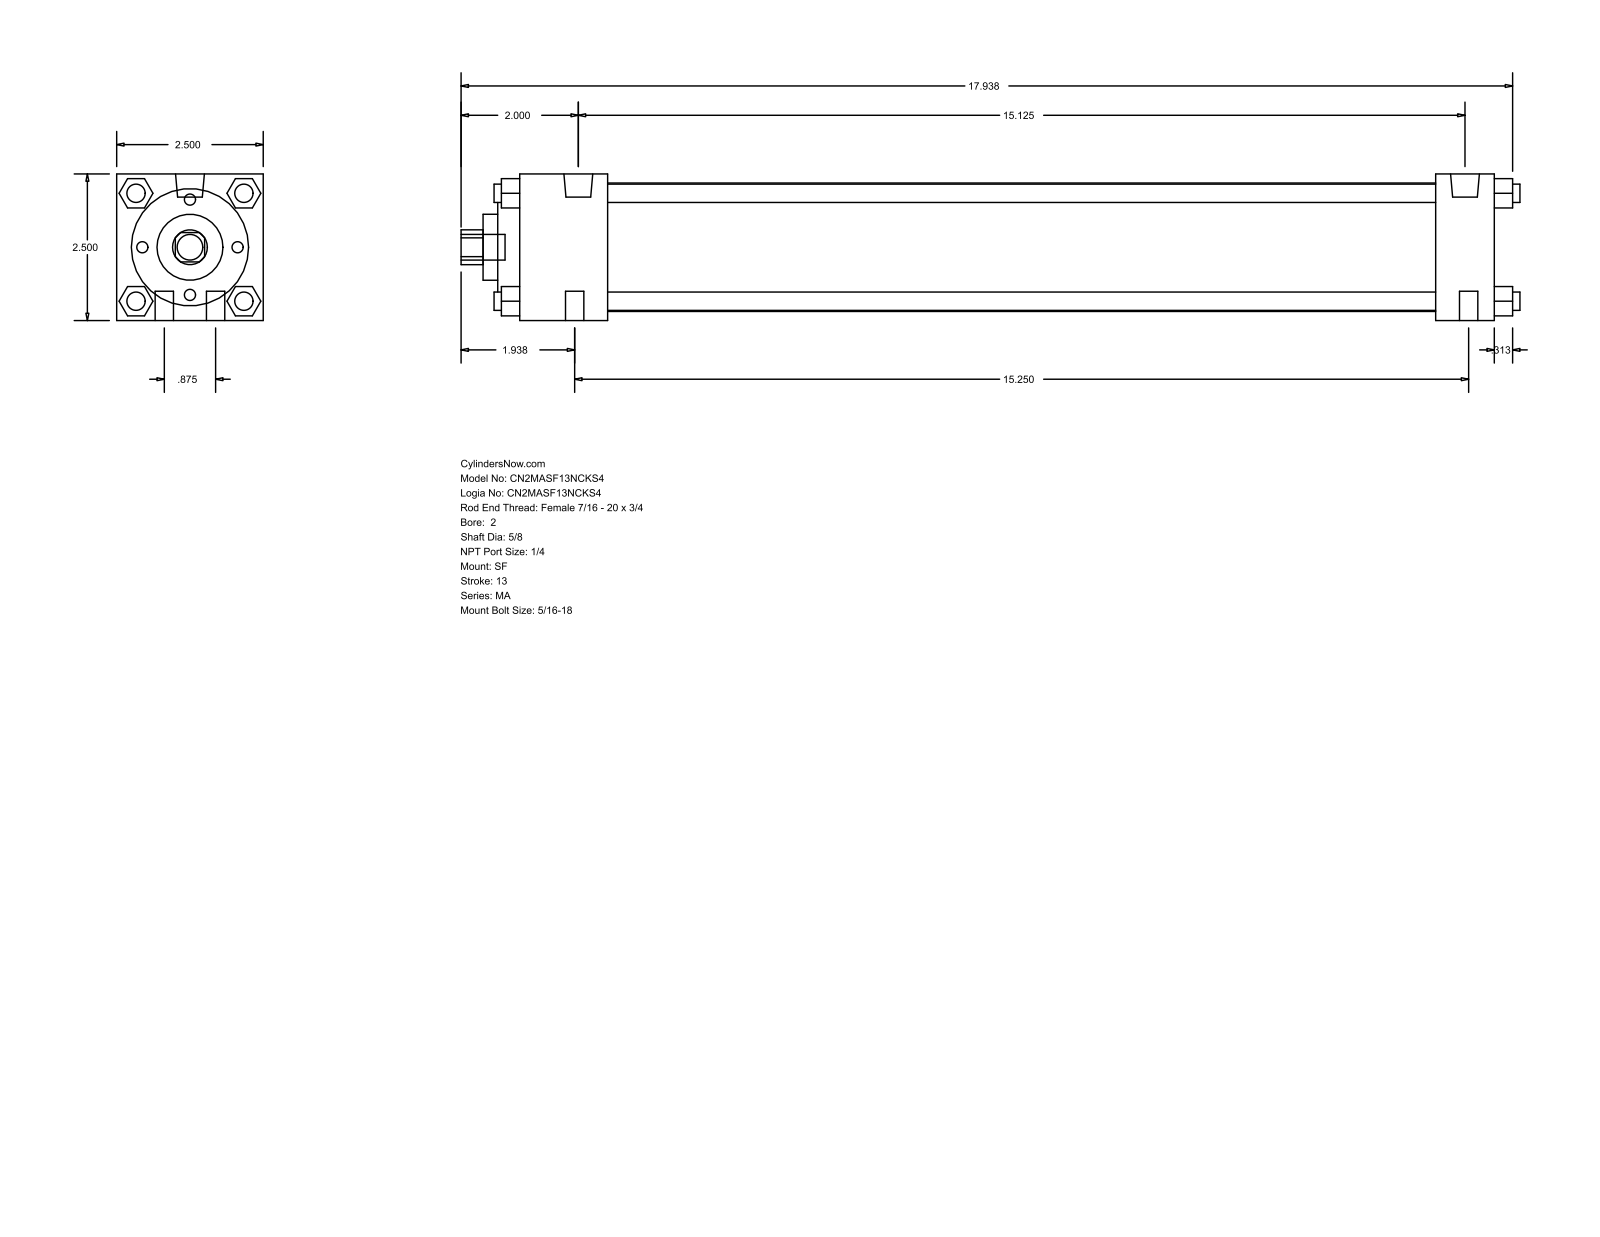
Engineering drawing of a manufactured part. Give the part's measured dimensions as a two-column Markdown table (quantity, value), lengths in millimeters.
| quantity | value |
| --- | --- |
| part name | MA_SF__0200_0.625 |
| STEP written by | GSSL Pune (CONFIG_CONTROL_DESIGN) |
| units | millimeters |
| bodies | 0 solids, 126 faces (95 planar, 31 cylindrical, 0 other) |
| overall size | 458.79 × 63.5 × 63.5 |
| round holes (diameter × count) | 15.88 × 1, 28.57 × 1, 50.8 × 1, 55.63 × 1 |
| round bosses / shafts (diameter × count) | 7.94 × 10, 12.49 × 2, 11.11 × 1 |
| partial cylindrical surfaces (radius × count) | 7.54 × 1 |
| main face-to-face distances | 63.5, 12.7, 38.1, 9.52, 422.28, 396.87, 25.41, 358.77, 384.18, 47.62 |
